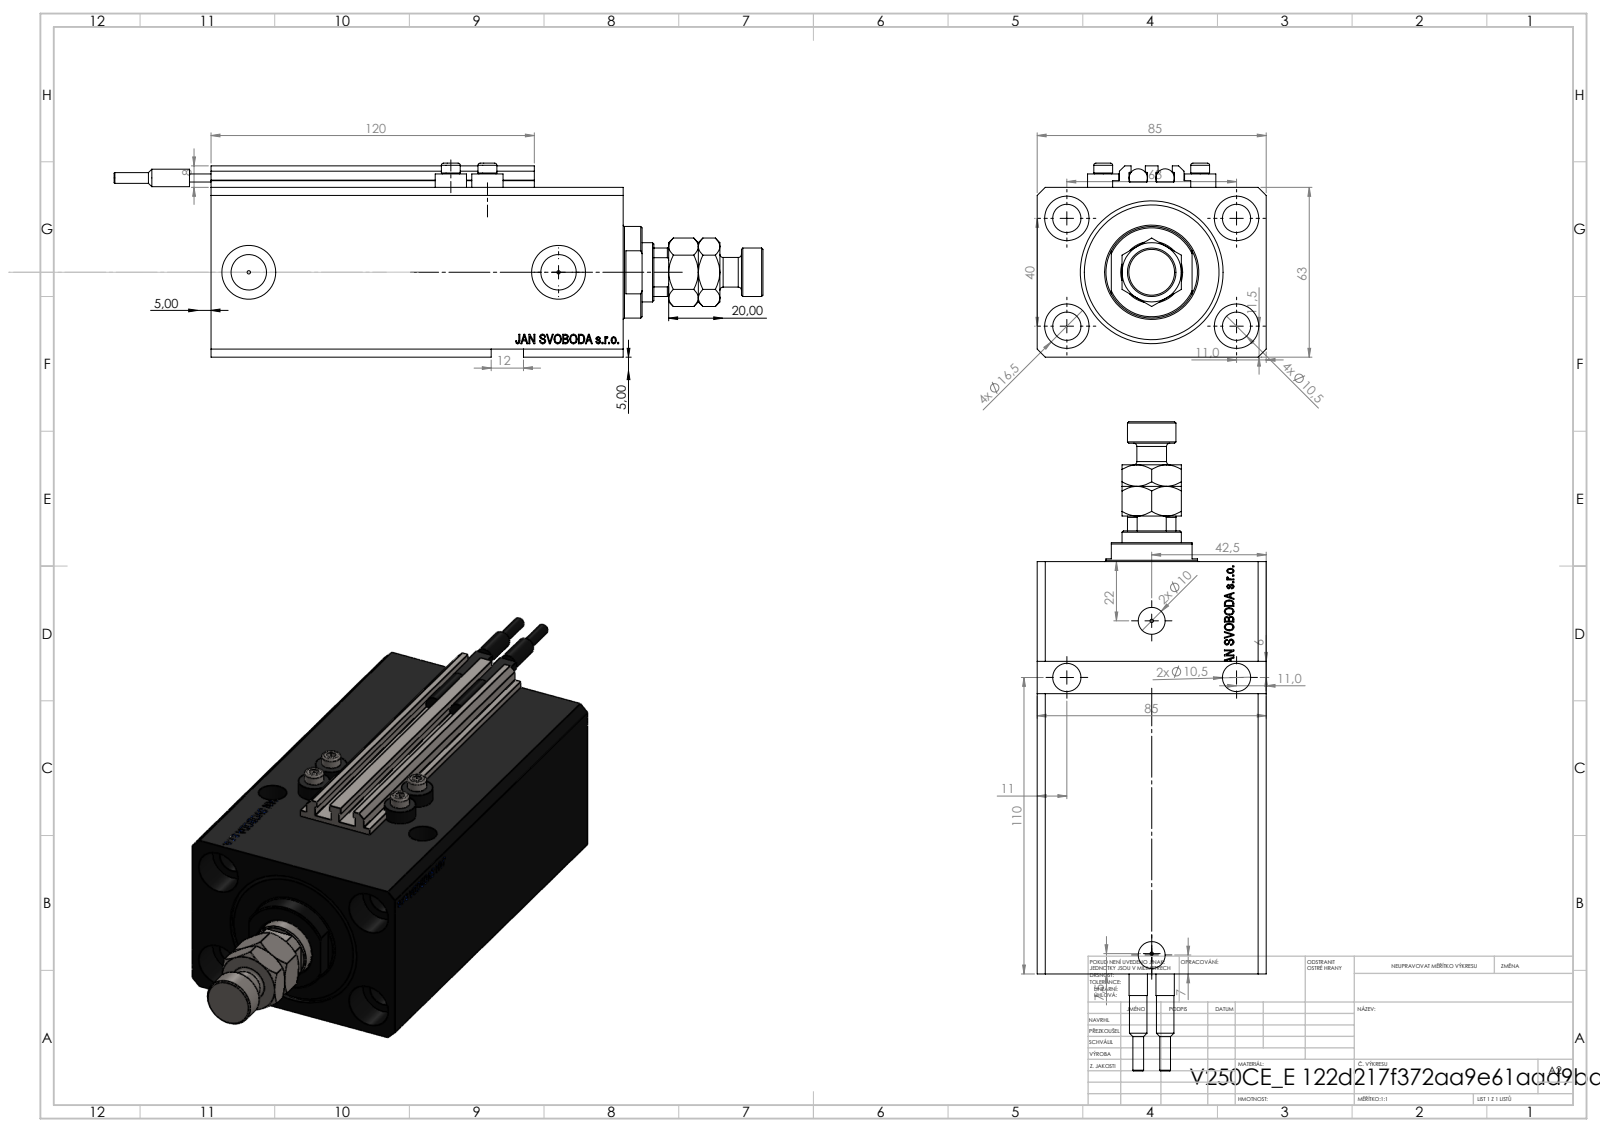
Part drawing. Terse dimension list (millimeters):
name: ALLEN BOLT V250CE; V250CE_E_Body; SWITCH_V250CE; MFA (+2 more)
written by: SolidWorks 2019 (CONFIG_CONTROL_DESIGN)
unit: mm
bodies: 11 solids, 1211 faces (583 planar, 162 cylindrical, 466 other)
size: 241 × 85 × 72
volume: 698 110 mm³; area: 146 803 mm²
holes: 8× ⌀10.5, 4× ⌀1.25, 4× ⌀4, 4× ⌀16.5, 2× ⌀10, 2× ⌀13.16, 2× ⌀20, 1× ⌀12.5, 1× ⌀22, 1× ⌀40, 1× ⌀53
bosses: 4× ⌀11.6, 4× ⌀7, 2× ⌀6.8, 2× ⌀6.5, 2× ⌀4, 1× ⌀34, 1× ⌀18, 1× ⌀11
rounds: 10× R0.2, 1× R10.5
face distances: 63, 85, 17, 153, 136, 65, 3, 11.4, 124.6, 141.6
hole spacings: 37.31, 63, 13.6, 15.4, 24.96, 33.62, 36, 37.86
